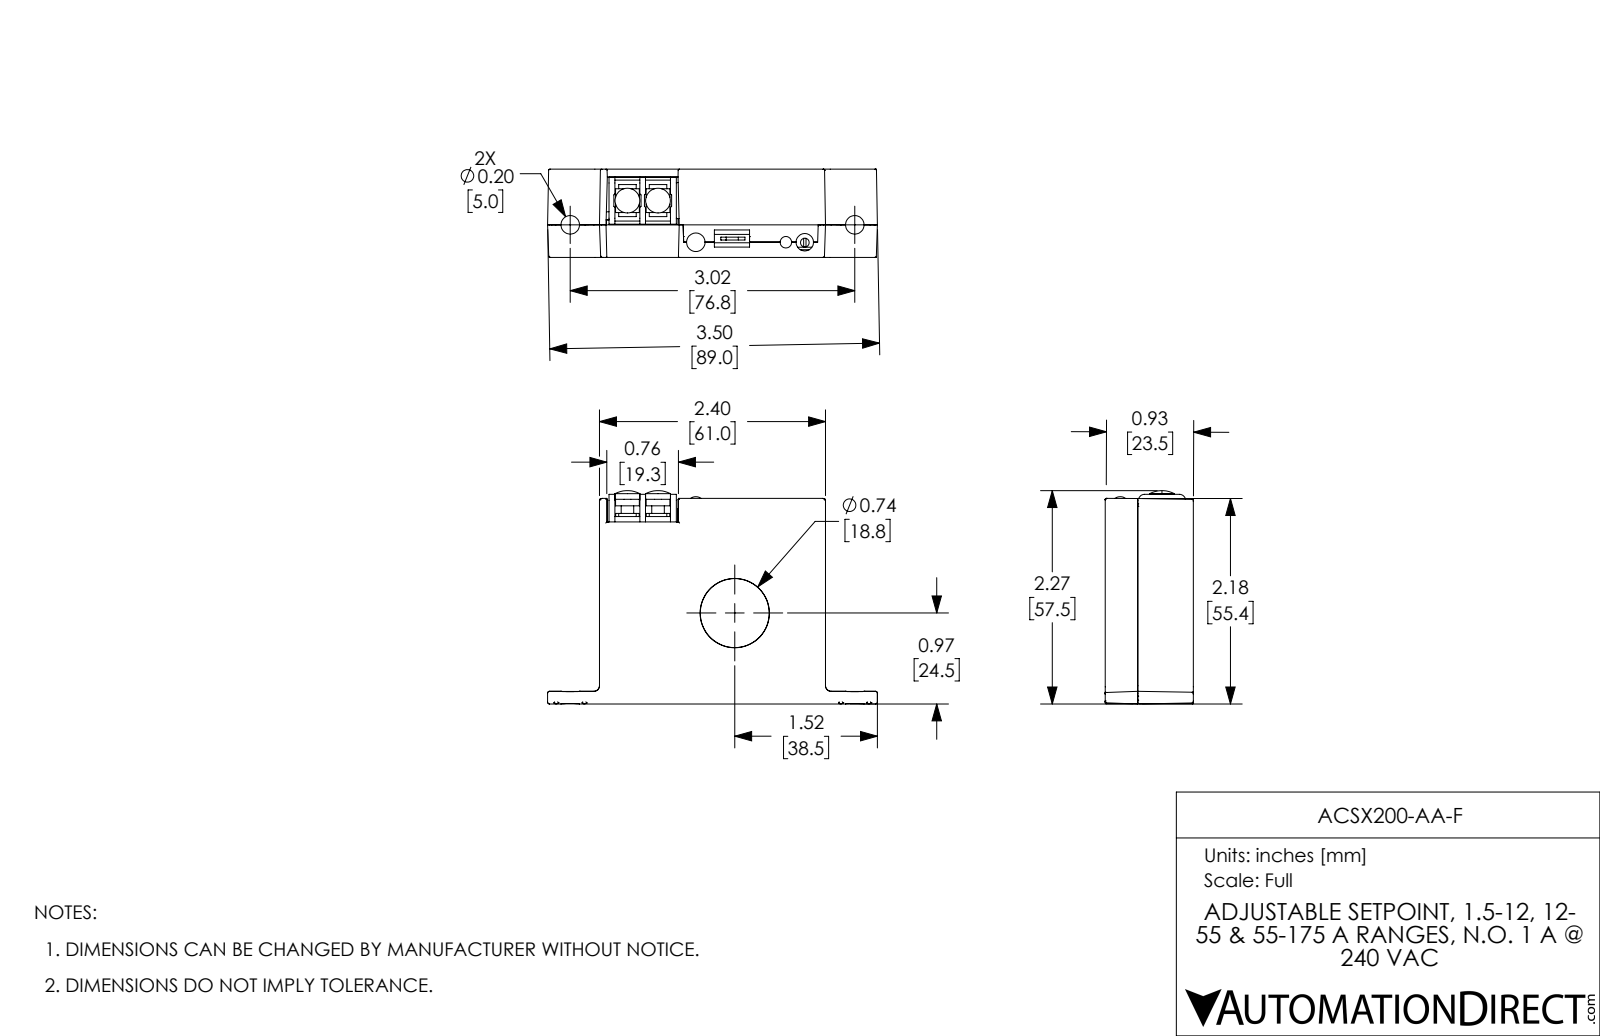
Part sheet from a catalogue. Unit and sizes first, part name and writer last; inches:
Units: inches
Overall size (bounding box): 3.504 × 2.265 × 0.937
Round holes (diameter × count): ⌀0.045 ×4, ⌀0.197 ×3, ⌀0.147 ×2, ⌀0.122 ×1, ⌀0.185 ×1, ⌀0.82 ×1
Round bosses / shafts (diameter × count): ⌀0.043 ×4, ⌀0.263 ×2, ⌀0.134 ×2, ⌀0.807 ×1, ⌀0.234 ×1, ⌀0.194 ×1, ⌀0.093 ×1
Partial cylindrical surfaces — rounded edges, fillets, slot ends (radius × count): R0.012 ×20, R0.02 ×12, R0.03 ×8, R0.059 ×4, R0.008 ×2, R0.063 ×2
Main face-to-face distances: 0.083, 0.854, 0.937, 0.772, 0.442, 0.349, 0.413, 0.266, 0.33, 0.064
Hole centre spacings: 2.151, 3.535, 0.201, 0.325, 0.563, 0.598, 0.66, 0.755
Volume: 1.893 in³ · Surface area: 53.16 in²
Bodies: 8 solids, 550 faces (360 planar, 126 cylindrical, 64 other)
Part name (STEP PRODUCT): ACSX200-AA-F
STEP written by: SolidWorks 2017 (AUTOMOTIVE_DESIGN)
